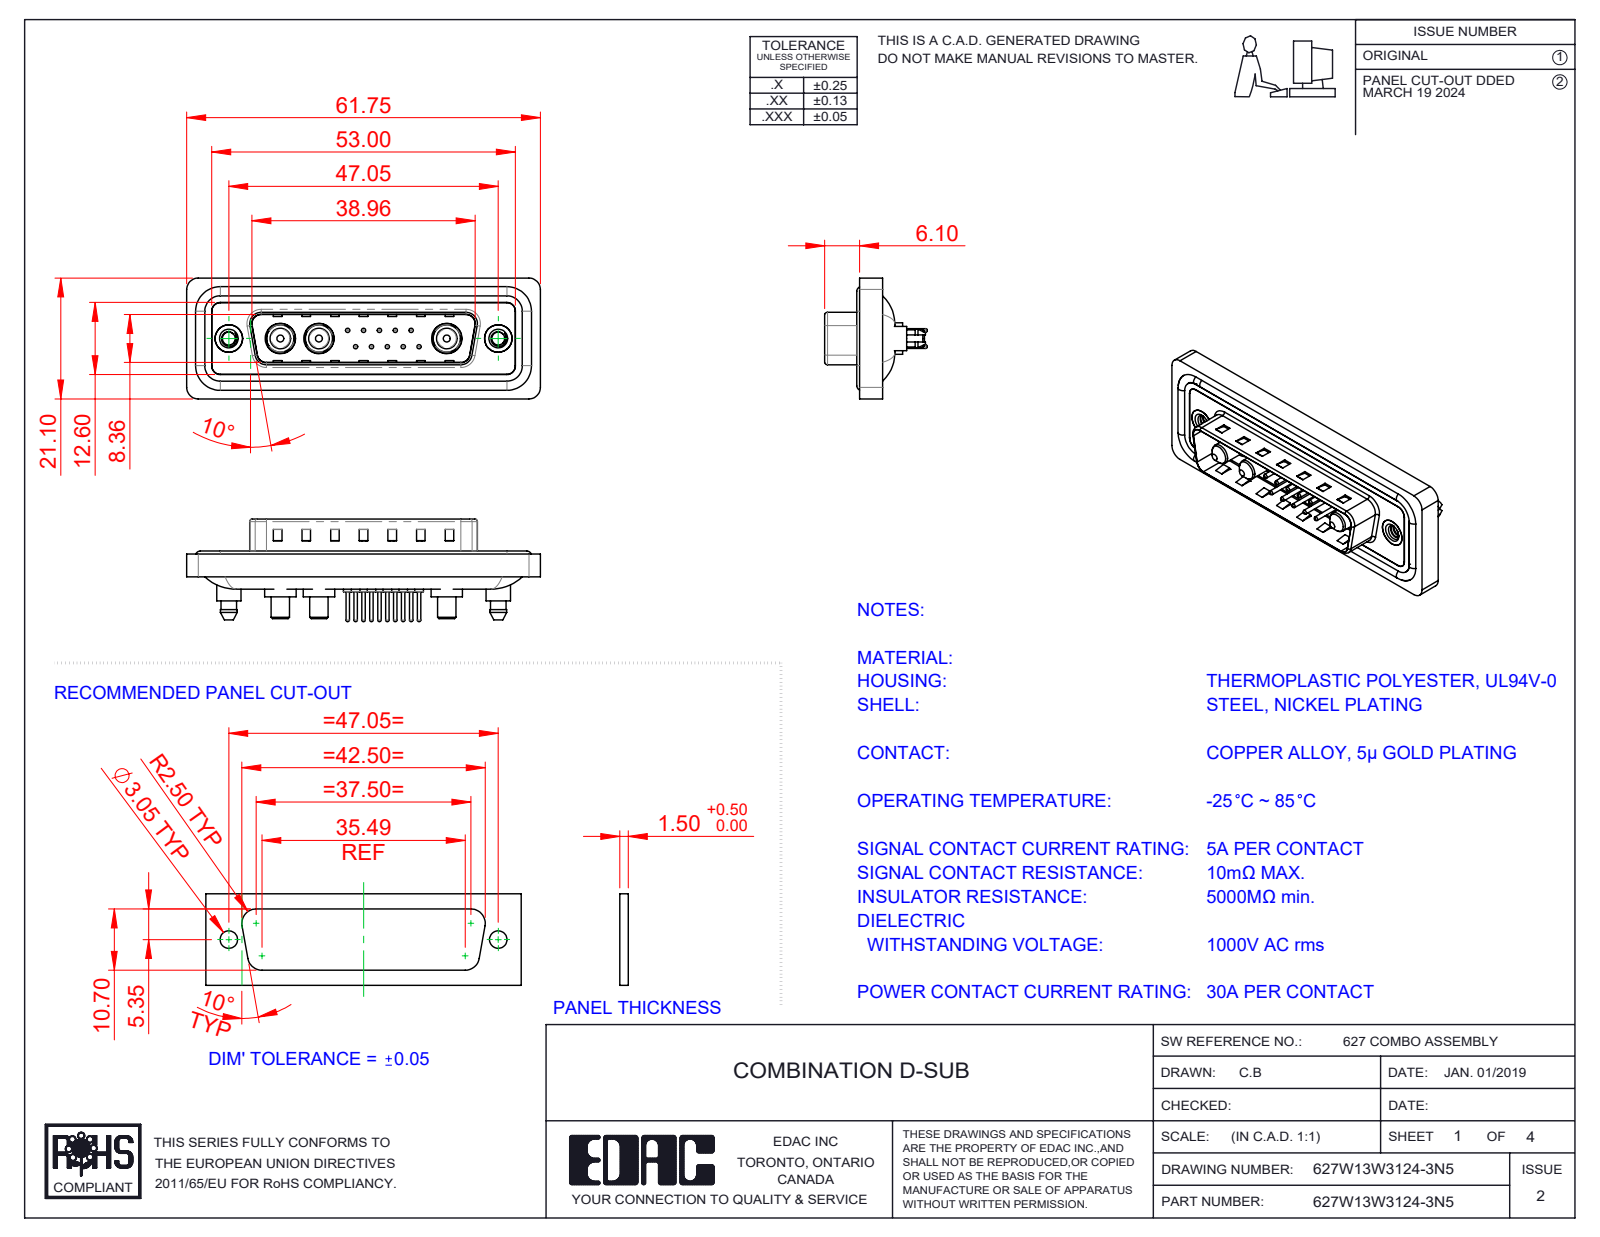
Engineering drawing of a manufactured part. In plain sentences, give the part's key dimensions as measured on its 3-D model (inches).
The part is named "627Combo Contact Row 1_24; 627Combo Threaded Boardlock_5; 627Combo Shell Front_25 Contacts; 627W13W3124-3N5 (+5 more)". Its 3-D file was written by "SolidWorks 2023 (CONFIG_CONTROL_DESIGN)". It is 23 solids with 1020 faces: 325 planar, 417 cylindrical and 278 other. Overall it measures 2.431 by 0.831 by 0.705 inches. Its volume is 0.457 cubic inches and its surface area 18.94 square inches. Round holes: 10 of diameter 0.03, 10 of diameter 0.063, 10 of diameter 0.079, 3 of diameter 0.191, 3 of diameter 0.209, 2 of diameter 0.089, 2 of diameter 0.157, 2 of diameter 0.189, 2 of diameter 0.197. Round bosses or shafts: 10 of diameter 0.059, 10 of diameter 0.024, 4 of diameter 0.063, 3 of diameter 0.217, 3 of diameter 0.205, 3 of diameter 0.187, 3 of diameter 0.148, 3 of diameter 0.142. Partial cylindrical surfaces (rounded edges, fillets, slot ends): 24 of radius 0.059, 18 of radius 0.079, 10 of radius 0.063, 8 of radius 0.02, 4 of radius 0.01, 4 of radius 0.024, 4 of radius 0.026, 4 of radius 0.035. The main face-to-face distances are 0.016, 0.059, 0.043, 0.063, 0.02, 0.122, 0.114, 0.032, 0.377, 0.161. The hole center spacings are 0.124, 0.109, 0.198, 0.218, 0.295, 0.198, 0.327, 0.398.
